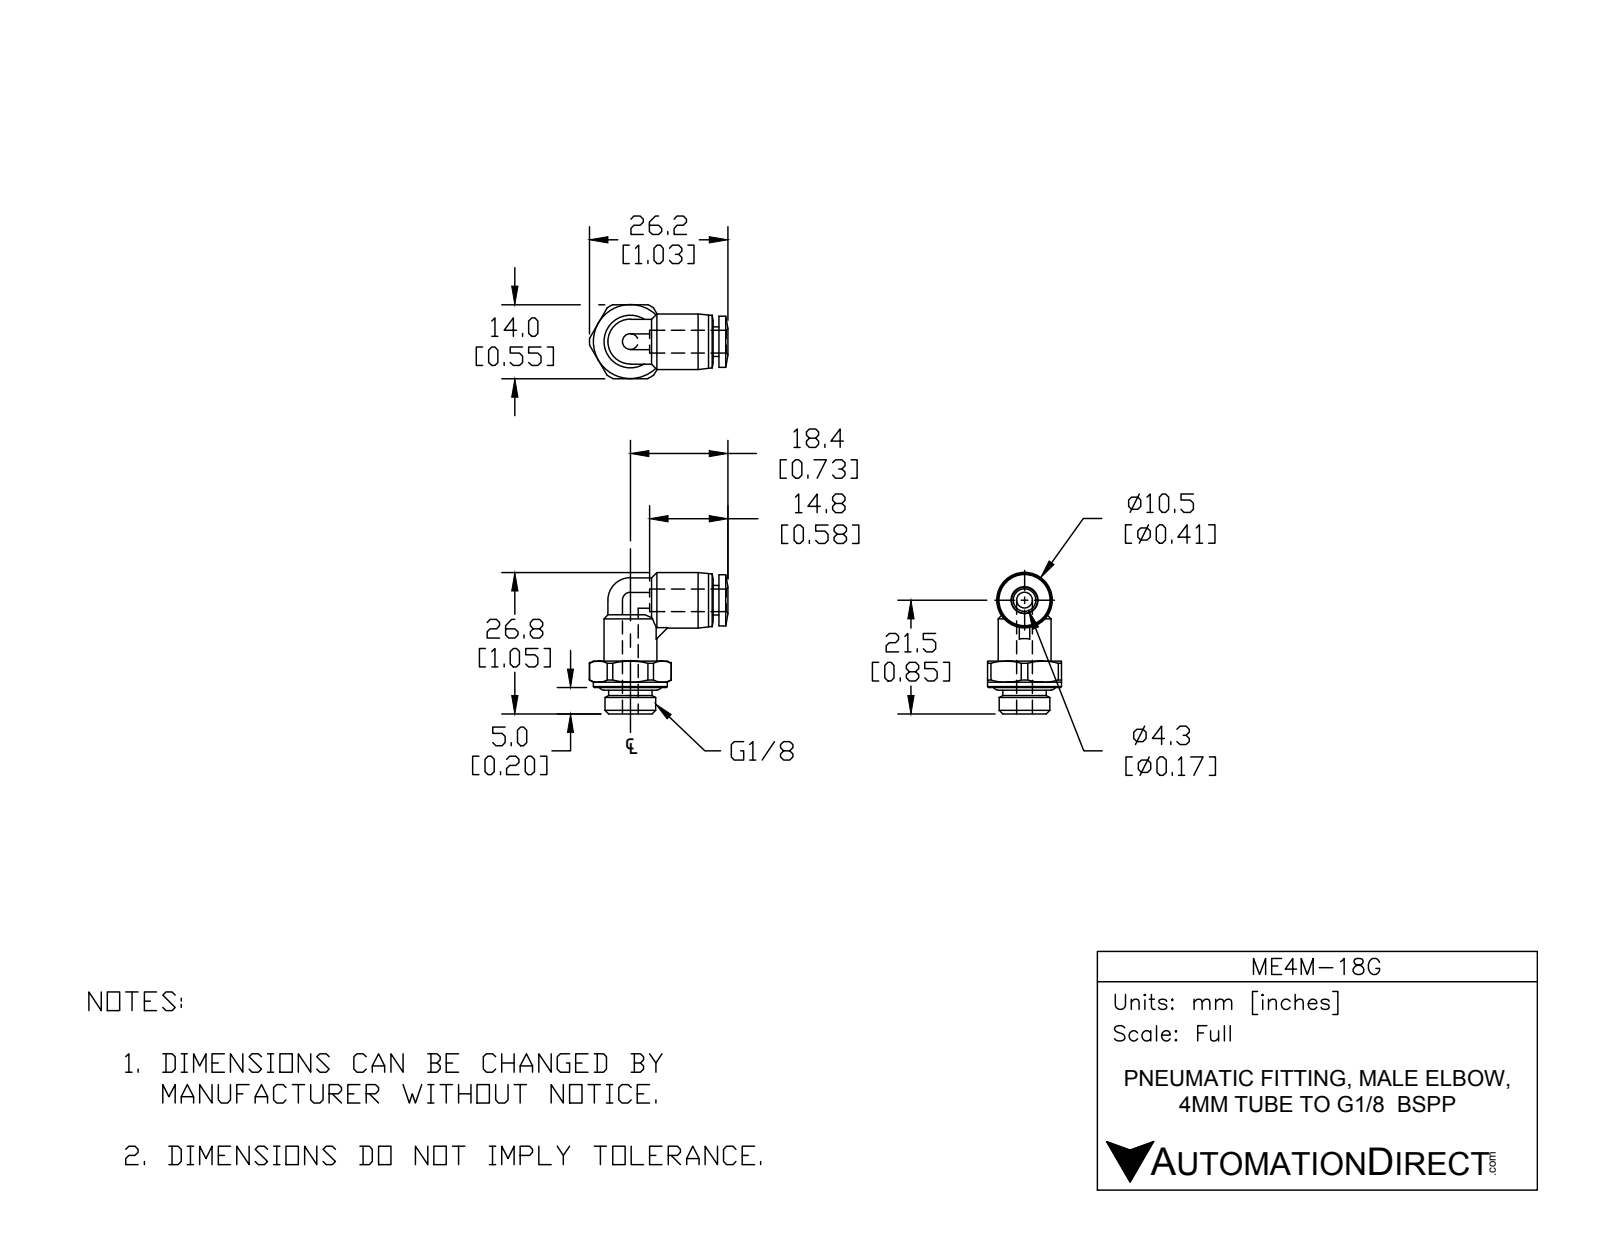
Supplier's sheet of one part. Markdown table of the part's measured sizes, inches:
| quantity | value |
| --- | --- |
| part name | ME4M-18G |
| STEP written by | SolidWorks 2015 (AUTOMOTIVE_DESIGN) |
| units | inches |
| bodies | 2 solids, 90 faces (18 planar, 33 cylindrical, 39 other) |
| overall size | 1.053 × 1.031 × 0.551 |
| volume | 0.178 in³ |
| surface area | 3.673 in² |
| round holes (diameter × count) | 0.118 × 2, 0.169 × 1 |
| round bosses / shafts (diameter × count) | 0.394 × 2, 0.551 × 1, 0.413 × 1, 0.382 × 1, 0.378 × 1, 0.323 × 1, 0.22 × 1 |
| partial cylindrical surfaces (radius × count) | 0.167 × 2, 0.305 × 1 |
| main face-to-face distances | 0.551, 0.142, 0.252, 0.394, 0.197, 0.043, 0.055, 0.472, 0.516, 0.236 |
